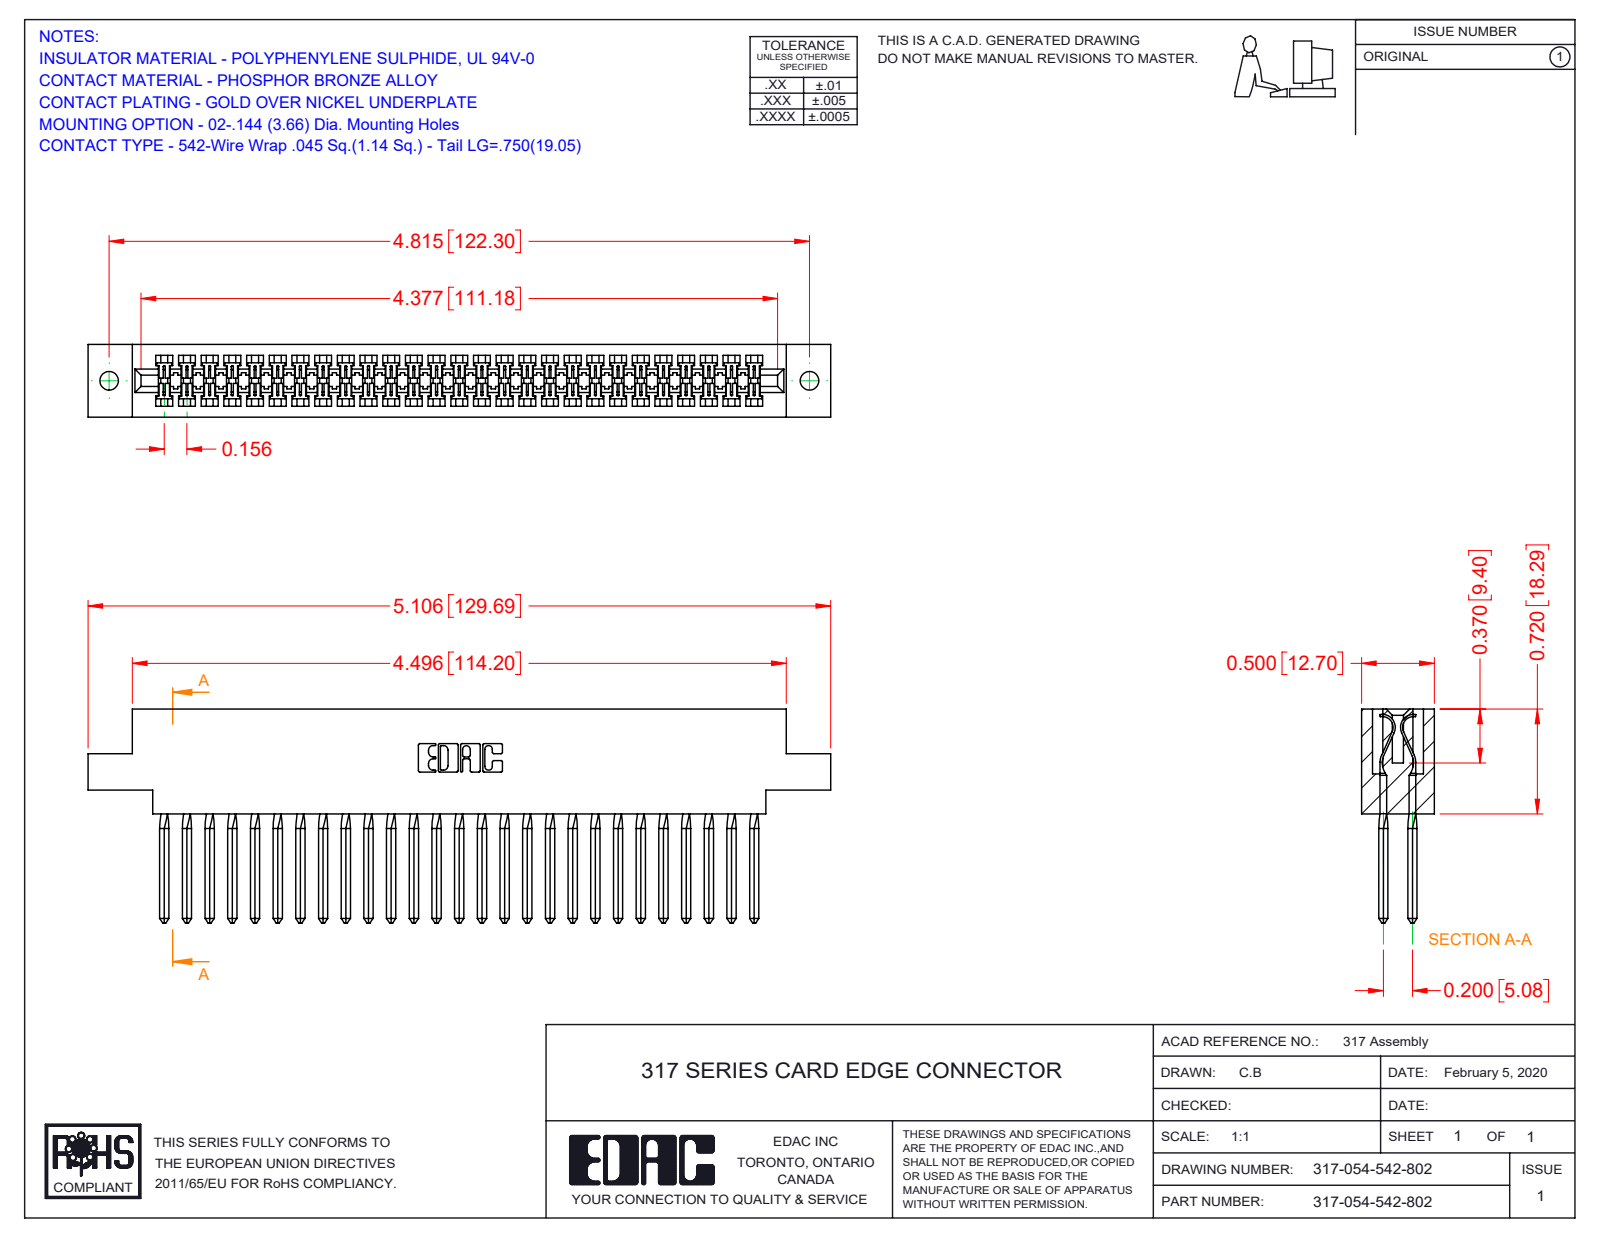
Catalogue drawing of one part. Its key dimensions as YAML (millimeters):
part_name: "317 Part_.144 Dia; 317-290-003_542; 317-054-542-802"
step_written_by: "SolidWorks 2016 (CONFIG_CONTROL_DESIGN)"
units: millimeters
bodies: {solids: 55, faces: 3180, planar: 2542, cylindrical: 422, other: 216}
overall_size: [129.7, 37.3, 12.7]
volume: 20730
surface_area: 28070
round_holes:
  - {diameter: 3.3, count: 2}
partial_cylinders:
  - {radius: 0.2, count: 108}
  - {radius: 0.3, count: 22}
  - {radius: 0.2, count: 6}
  - {radius: 0.8, count: 6}
  - {radius: 0.7, count: 3}
  - {radius: 1.9, count: 2}
  - {radius: 2.3, count: 2}
  - {radius: 2.5, count: 2}
face_to_face_distances: [12.7, 1.9, 10.8, 8.9, 5.1, 2.8, 2.9, 1.2, 18.3, 3.3]
hole_center_spacings: [122.3]
